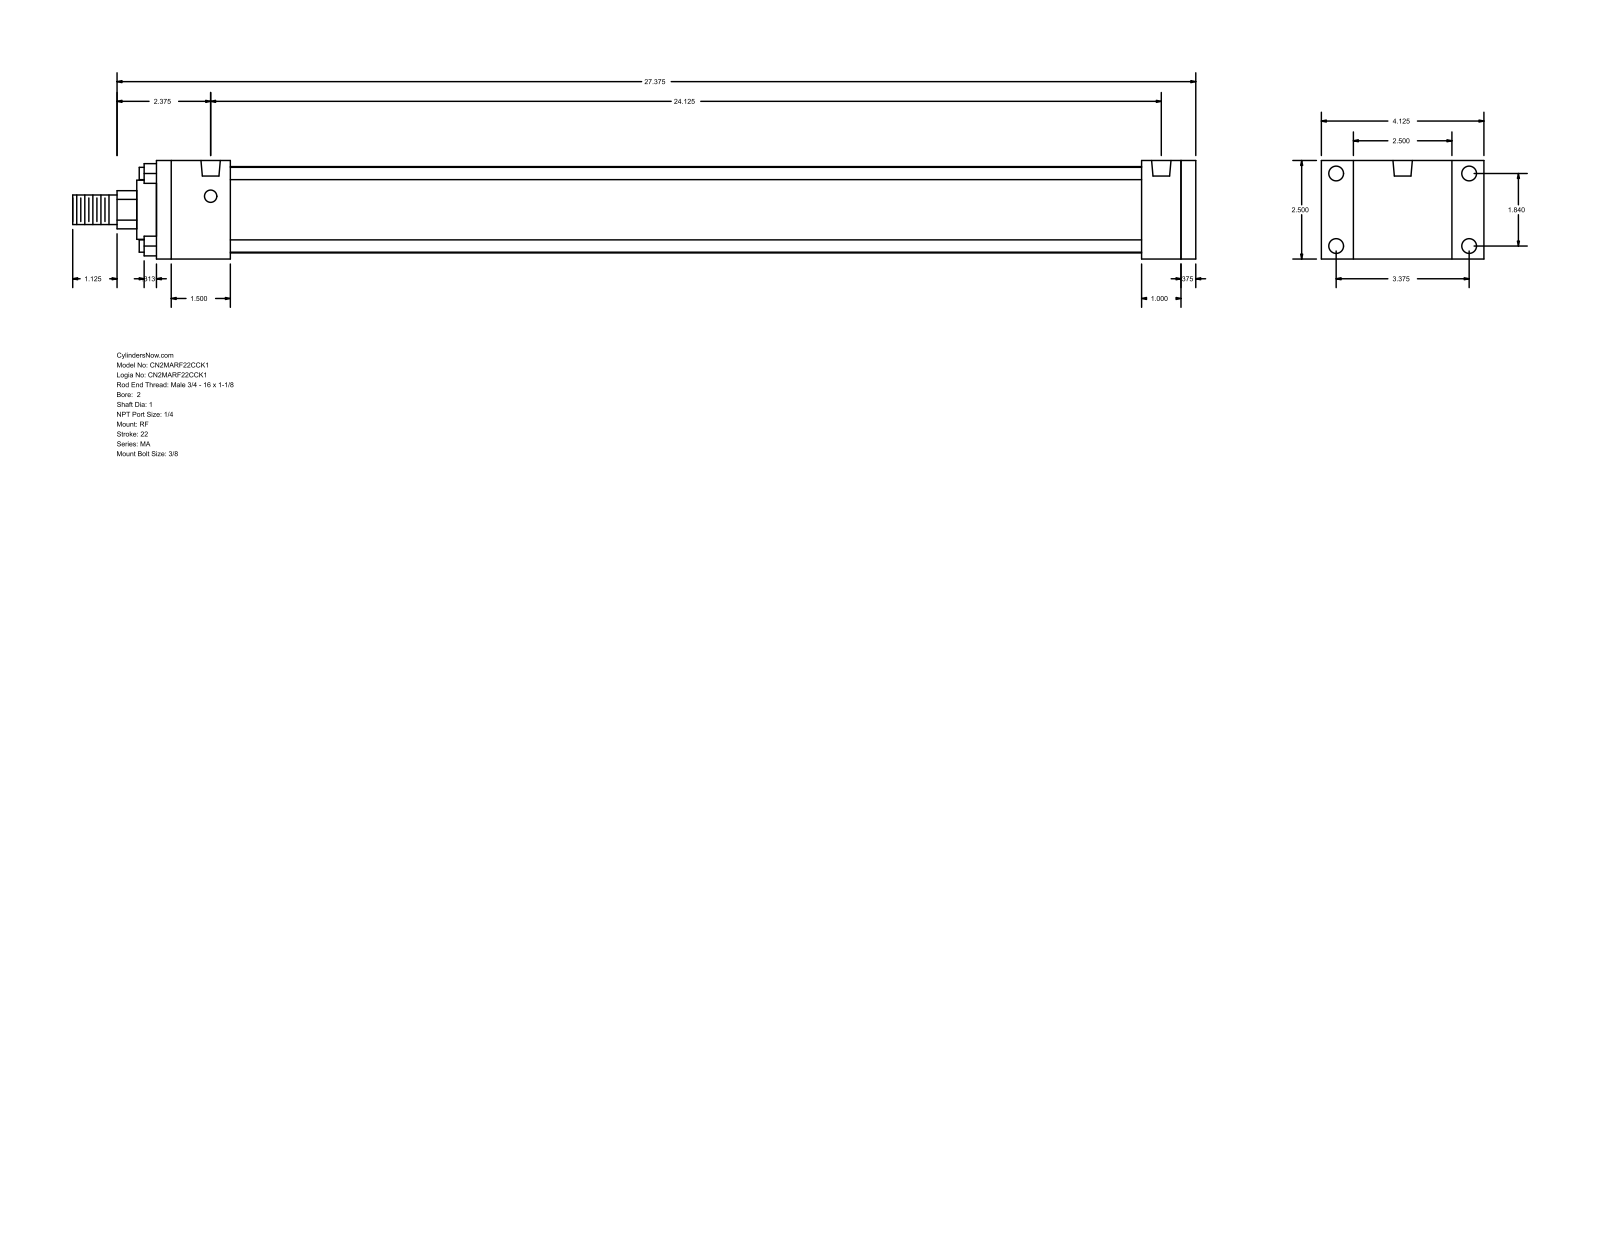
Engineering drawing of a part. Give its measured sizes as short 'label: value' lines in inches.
name: MA_RF__0200_1
written by: GSSL Pune (CONFIG_CONTROL_DESIGN)
unit: in
bodies: 0 solids, 92 faces (64 planar, 28 cylindrical, 0 other)
size: 28.5 × 4.125 × 2.5
holes: 4× ⌀0.313, 4× ⌀0.375, 2× ⌀0.492
bosses: 4× ⌀0.313, 1× ⌀2.19, 1× ⌀1.5, 1× ⌀1, 1× ⌀0.75
rounds: 1× R0.484
face distances: 2.5, 26, 0.375, 26.375, 1, 0.813, 0.5, 1.875, 24.125, 24.5
hole spacings: 1.84, 3.375, 3.844, 24.125
